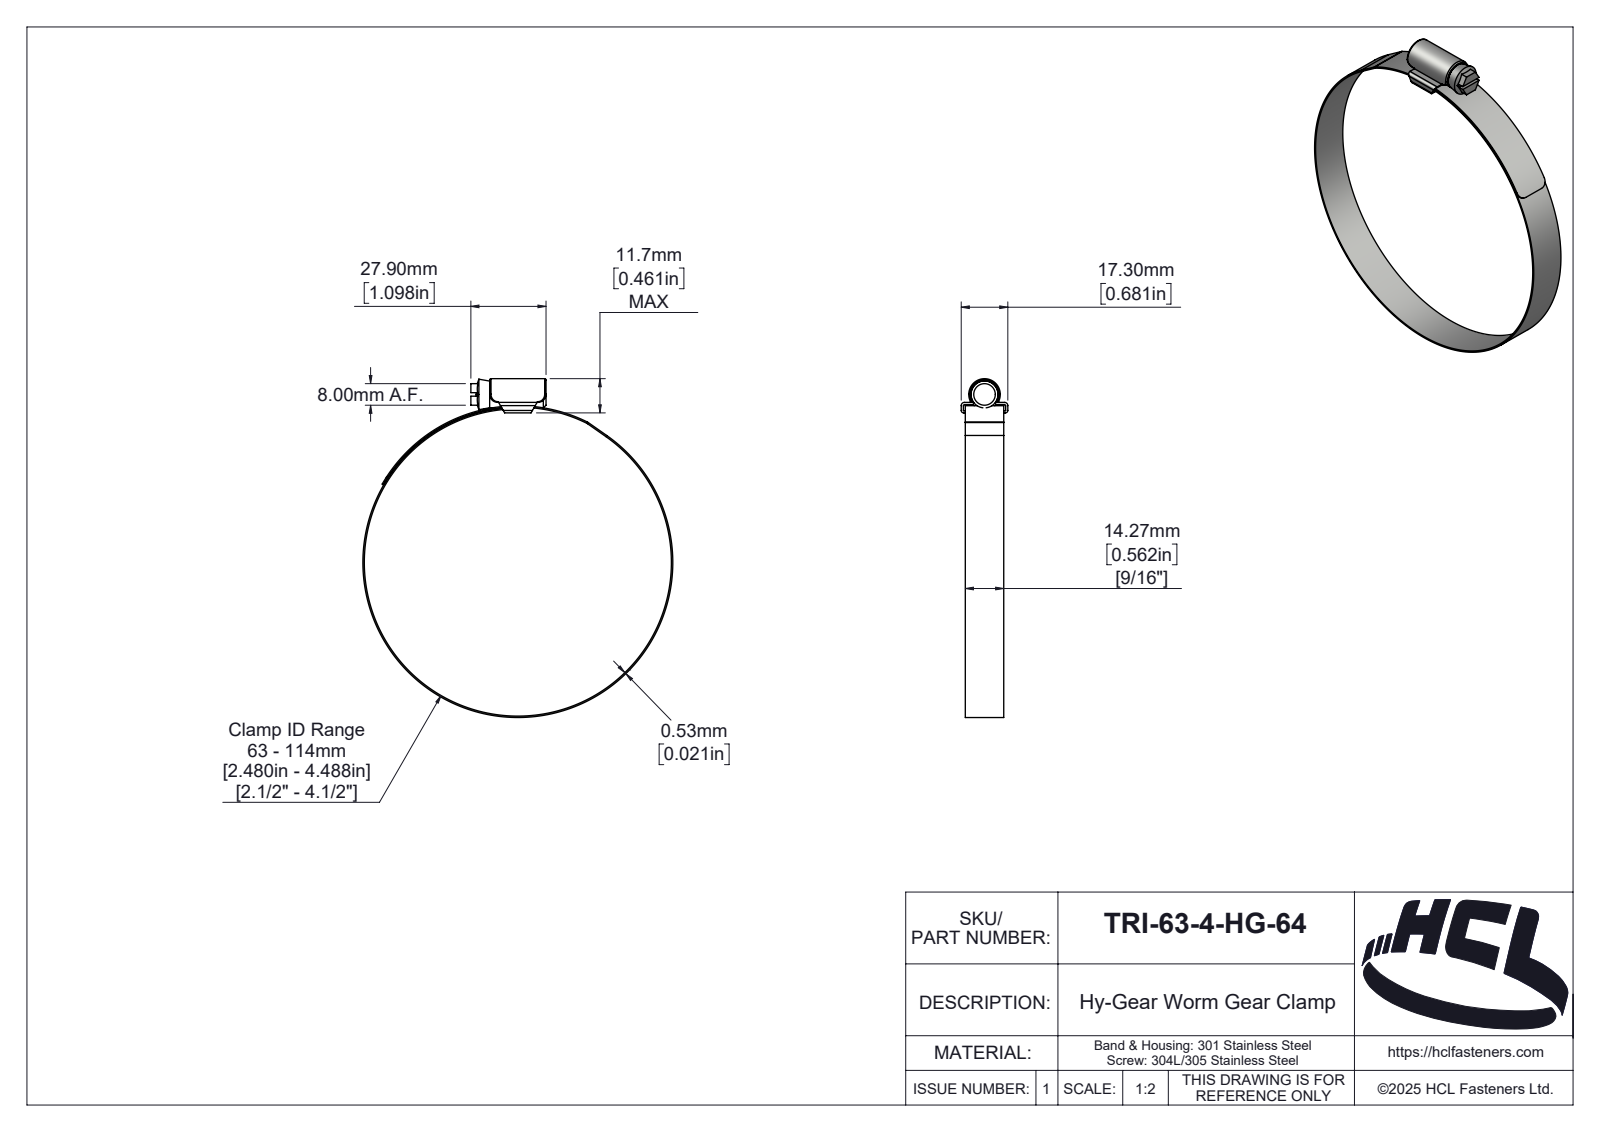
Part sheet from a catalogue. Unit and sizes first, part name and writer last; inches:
Units: inches
Overall size (bounding box): 4.95 × 4.53 × 0.681
Round holes (diameter × count): ⌀4.488 ×1
Round bosses / shafts (diameter × count): ⌀4.53 ×1, ⌀0.394 ×1
Partial cylindrical surfaces — rounded edges, fillets, slot ends (radius × count): R0.02 ×6, R0.118 ×4, R0.004 ×2, R0.035 ×2, R0.047 ×2, R0.018 ×1, R0.074 ×1, R0.079 ×1
Main face-to-face distances: 0.031, 0.561, 0.122, 0.021, 0.091, 0.154, 1.098, 0.06, 0.621, 0.65
Volume: 0.364 in³ · Surface area: 23.64 in²
Bodies: 3 solids, 189 faces (39 planar, 89 cylindrical, 61 other)
Part name (STEP PRODUCT): TRI-50-0-HG-64
STEP written by: SolidWorks 2025 (AUTOMOTIVE_DESIGN)
